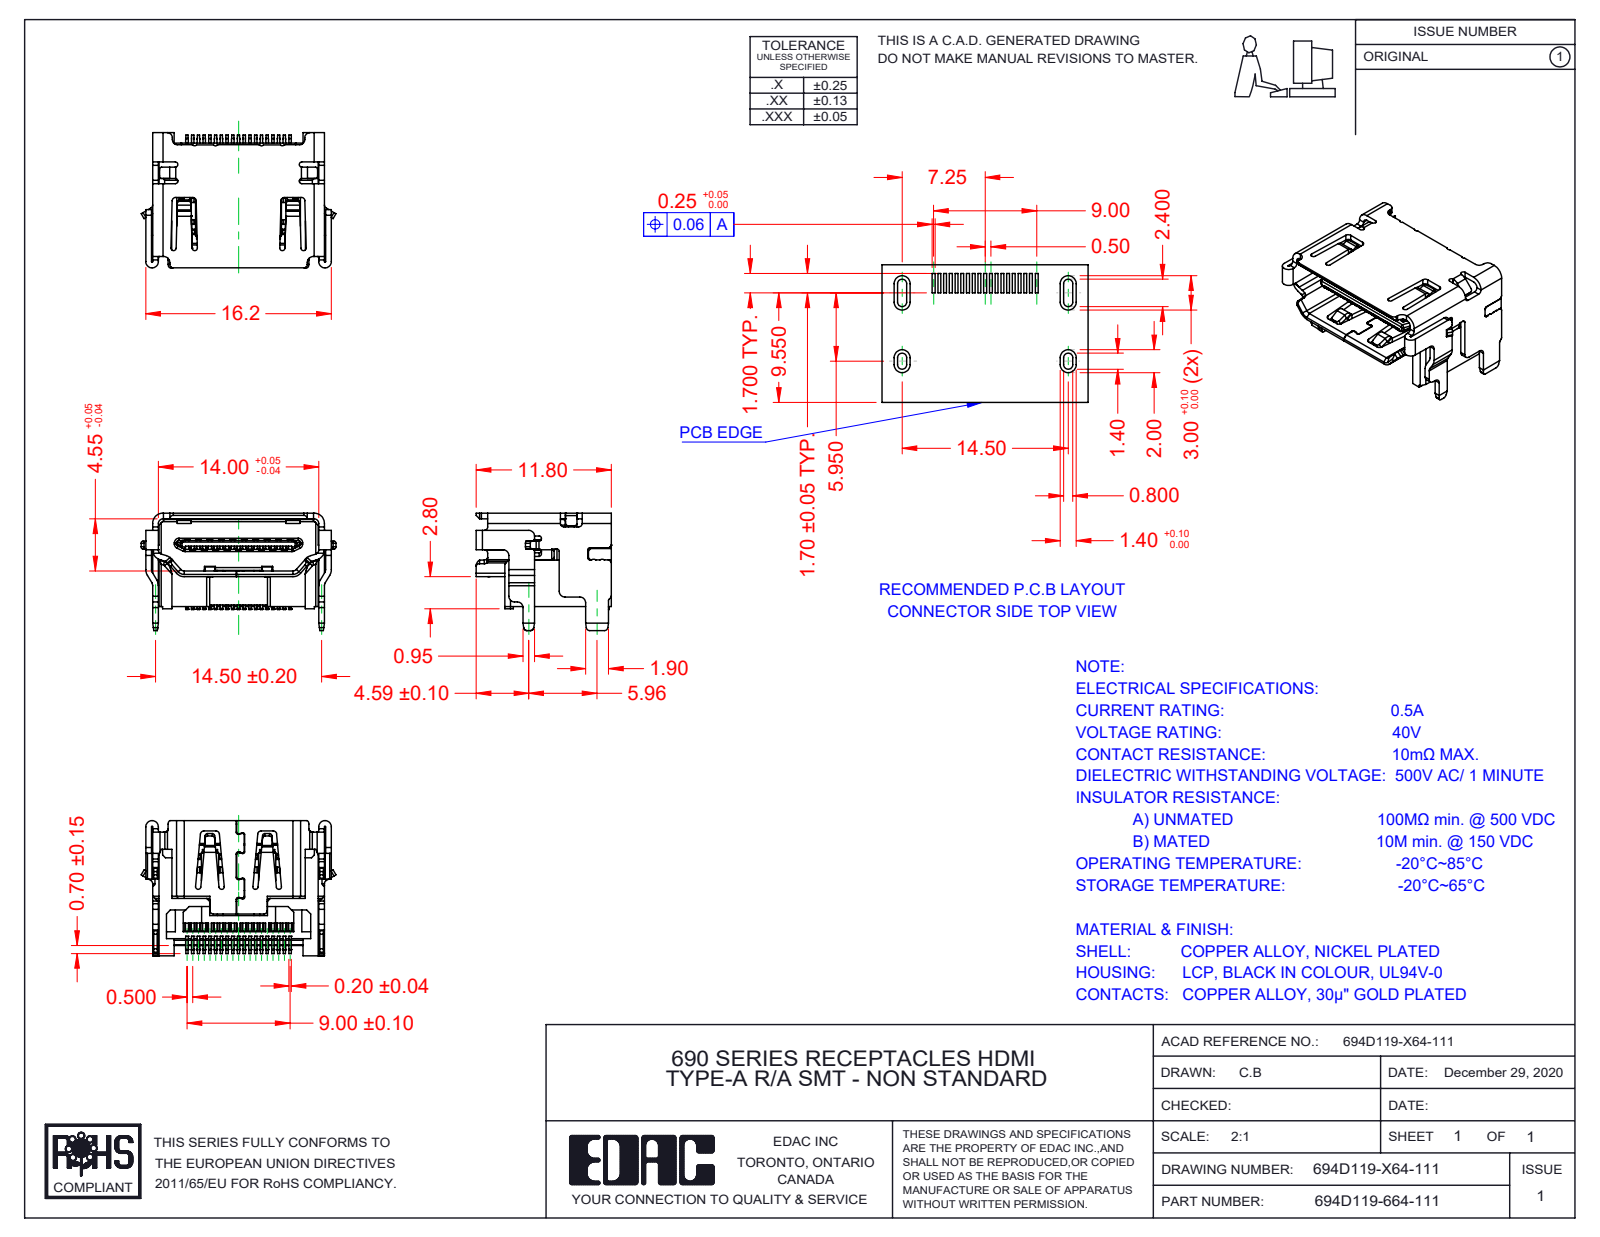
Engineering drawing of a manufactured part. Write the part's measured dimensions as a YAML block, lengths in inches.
part_name: "Shell 694D119-X64-111; Insulator 694D119-X64-111; Contact Upper 694D119-X64-111; 694D119-164-111 (+1 more)"
step_written_by: "SolidWorks 2020 (AUTOMOTIVE_DESIGN)"
units: inches
bodies: {solids: 21, faces: 3276, planar: 2261, cylindrical: 948, other: 67}
overall_size: [0.67, 0.465, 0.404]
volume: 0.034
surface_area: 3.438
partial_cylinders:
  - {radius: 0.008, count: 200}
  - {radius: 0.006, count: 96}
  - {radius: 0.004, count: 47}
  - {radius: 0.012, count: 34}
  - {radius: 0.004, count: 20}
  - {radius: 0.02, count: 15}
  - {radius: 0.009, count: 13}
  - {radius: 0.039, count: 10}
face_to_face_distances: [0.02, 0.02, 0.099, 0.022, 0.028, 0.571, 0.569, 0.549, 0.08, 0.199]
